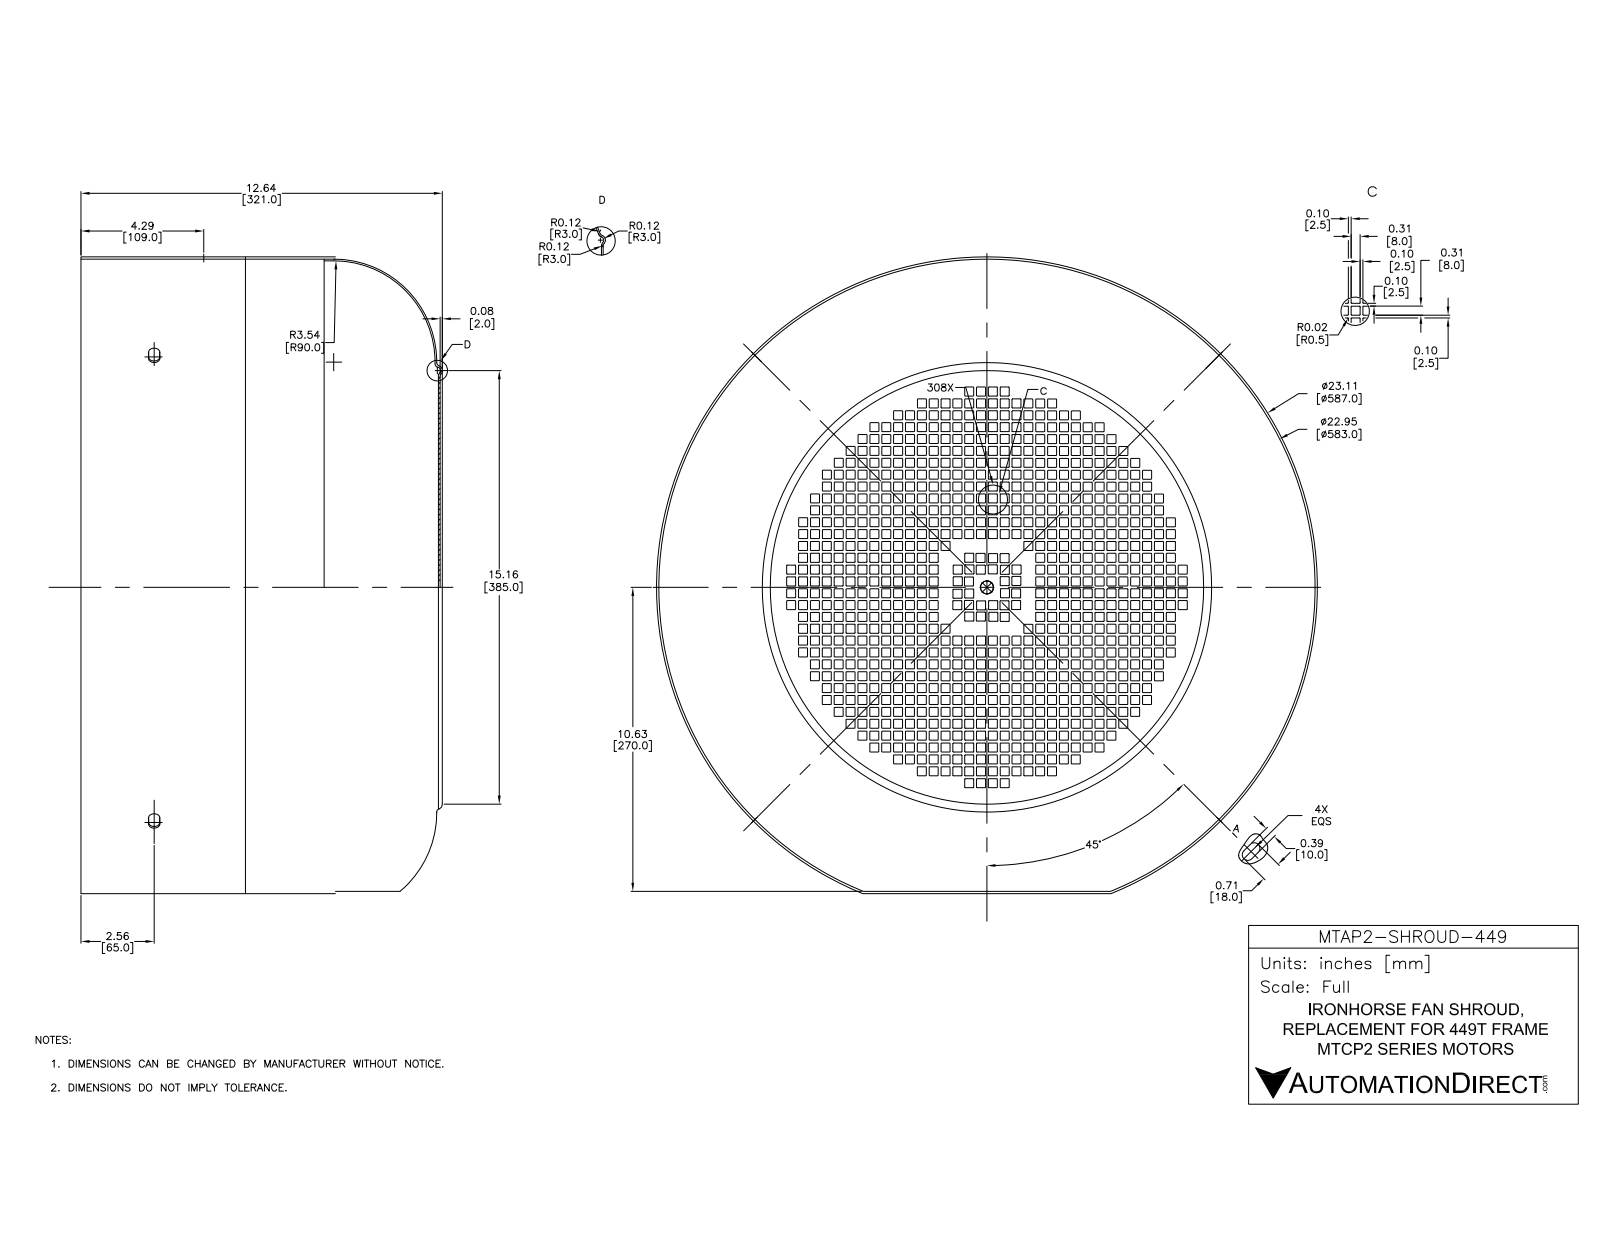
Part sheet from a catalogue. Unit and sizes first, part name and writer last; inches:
Units: inches
Overall size (bounding box): 23.11 × 23.088 × 12.283
Round holes (diameter × count): ⌀0.453 ×1, ⌀1.181 ×1, ⌀22.795 ×1, ⌀22.953 ×1
Round bosses / shafts (diameter × count): ⌀23.11 ×1, ⌀1.299 ×1, ⌀1.26 ×1, ⌀1.102 ×1
Partial cylindrical surfaces — rounded edges, fillets, slot ends (radius × count): R0.02 ×3360, R0.197 ×8
Main face-to-face distances: 0.079, 0.031, 0.047, 0.157, 2.48, 0.413, 1.24, 0.315, 0.394, 8.543
Volume: 90.76 in³ · Surface area: 2 459 in²
Bodies: 3 solids, 7628 faces (4222 planar, 3388 cylindrical, 18 other)
Part name (STEP PRODUCT): MTAP2-SHROUD-449
STEP written by: SolidWorks 2017 (AUTOMOTIVE_DESIGN)
